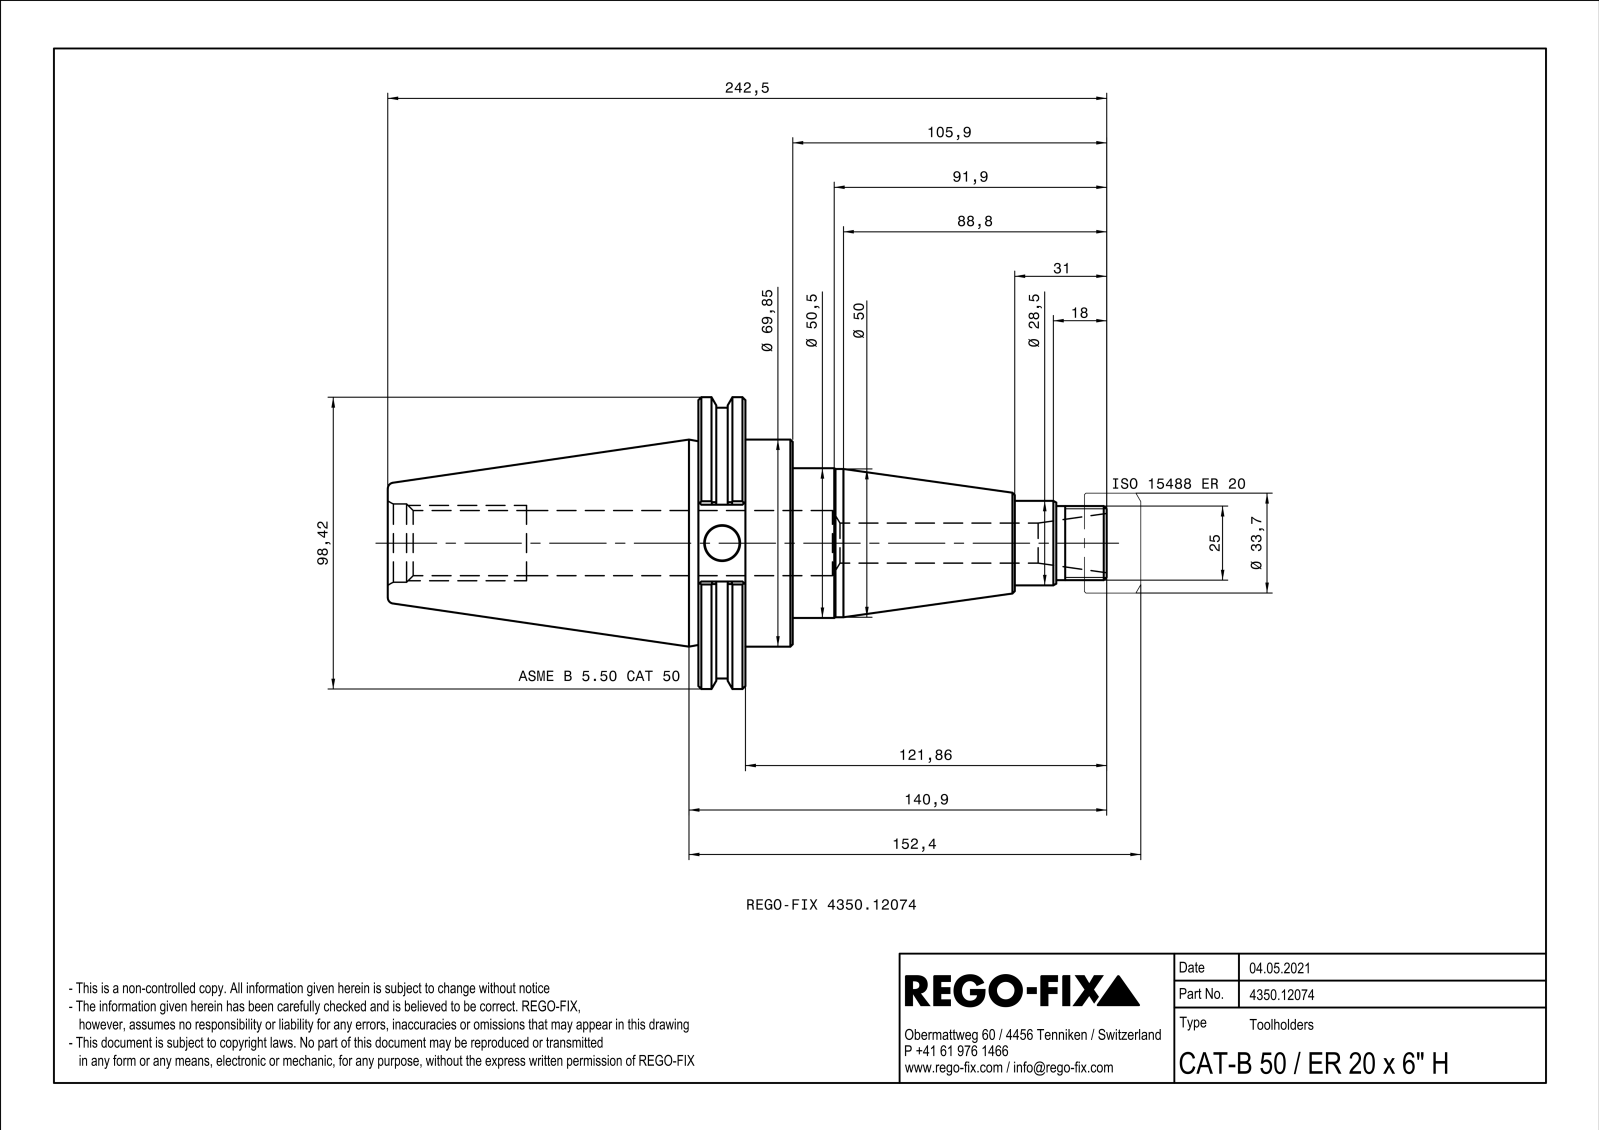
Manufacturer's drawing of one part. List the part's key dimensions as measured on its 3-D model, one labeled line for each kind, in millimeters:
Part name (STEP PRODUCT): NOCUT
STEP written by: SIEMENS PLM Software Solid Edge ST10 (AUTOMOTIVE_DESIGN)
Units: millimetres
Bodies: 1 solid, 134 faces (37 planar, 44 cylindrical, 53 other)
Overall size (bounding box): 242.5 × 98.42 × 94.39
Volume: 482 760 mm³ · Surface area: 66 531 mm²
Round holes (diameter × count): ⌀3.24 ×2, ⌀3.9 ×2, ⌀11.7 ×1, ⌀13.5 ×1, ⌀21.96 ×1, ⌀21.96 ×1, ⌀26.4 ×1
Round bosses / shafts (diameter × count): ⌀98.42 ×1, ⌀91.3 ×1, ⌀69.85 ×1, ⌀50.5 ×1, ⌀50 ×1, ⌀28.5 ×1, ⌀25 ×1
Partial cylindrical surfaces — rounded edges, fillets, slot ends (radius × count): R0.5 ×12
Main face-to-face distances: 15.87, 15.96, 31.83, 136.6, 120.64, 104.77, 72.73, 25.92, 25.79, 9.83
